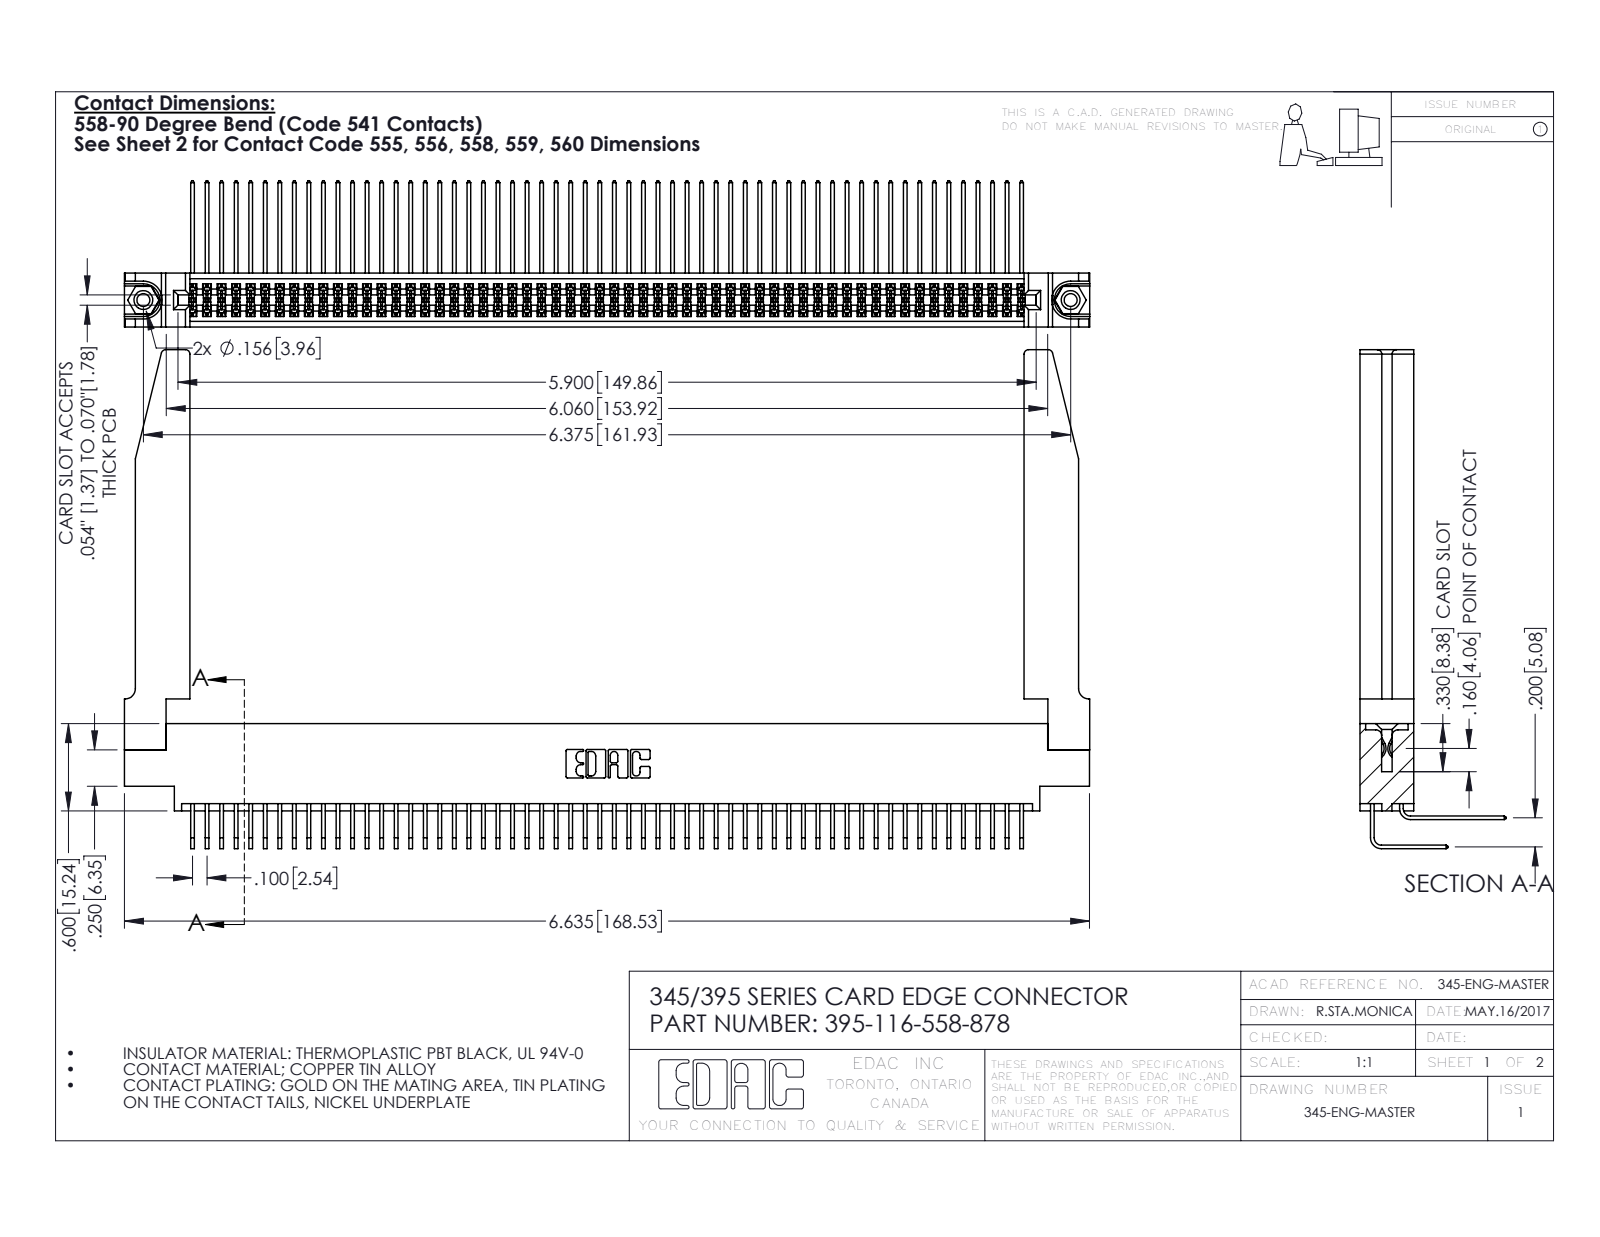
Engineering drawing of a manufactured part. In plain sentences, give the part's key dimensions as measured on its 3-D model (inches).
The part is named "345 Part_0.170 Offset - 0.156 Dia-TH; 345-292-001_558 559 Tail - 1; 345-292-001_558 Tail - 2; 345-250-001_345-250-001-102 (+2 more)". Its 3-D file was written by "SolidWorks 2016 (CONFIG_CONTROL_DESIGN)". It is 121 solids with 6396 faces: 4286 planar, 2058 cylindrical and 52 other. Overall it measures 6.636 by 3.429 by 1.005 inches. Its volume is 1.516 cubic inches and its surface area 55.31 square inches. Round holes: 2 of diameter 0.089, 2 of diameter 0.125, 2 of diameter 0.156, 1 of diameter 0.064. Round bosses or shafts: 2 of diameter 0.155. Partial cylindrical surfaces (rounded edges, fillets, slot ends): 174 of radius 0.006, 22 of radius 0.01, 8 of radius 0.03, 6 of radius 0.007, 6 of radius 0.031, 3 of radius 0.026, 2 of radius 0.014, 2 of radius 0.019. The main face-to-face distances are 0.072, 0.37, 0.298, 0.2, 0.098, 0.272, 0.025, 0.225, 0.175, 0.025. The hole center spacings are 0.27, 6.139, 6.375.
